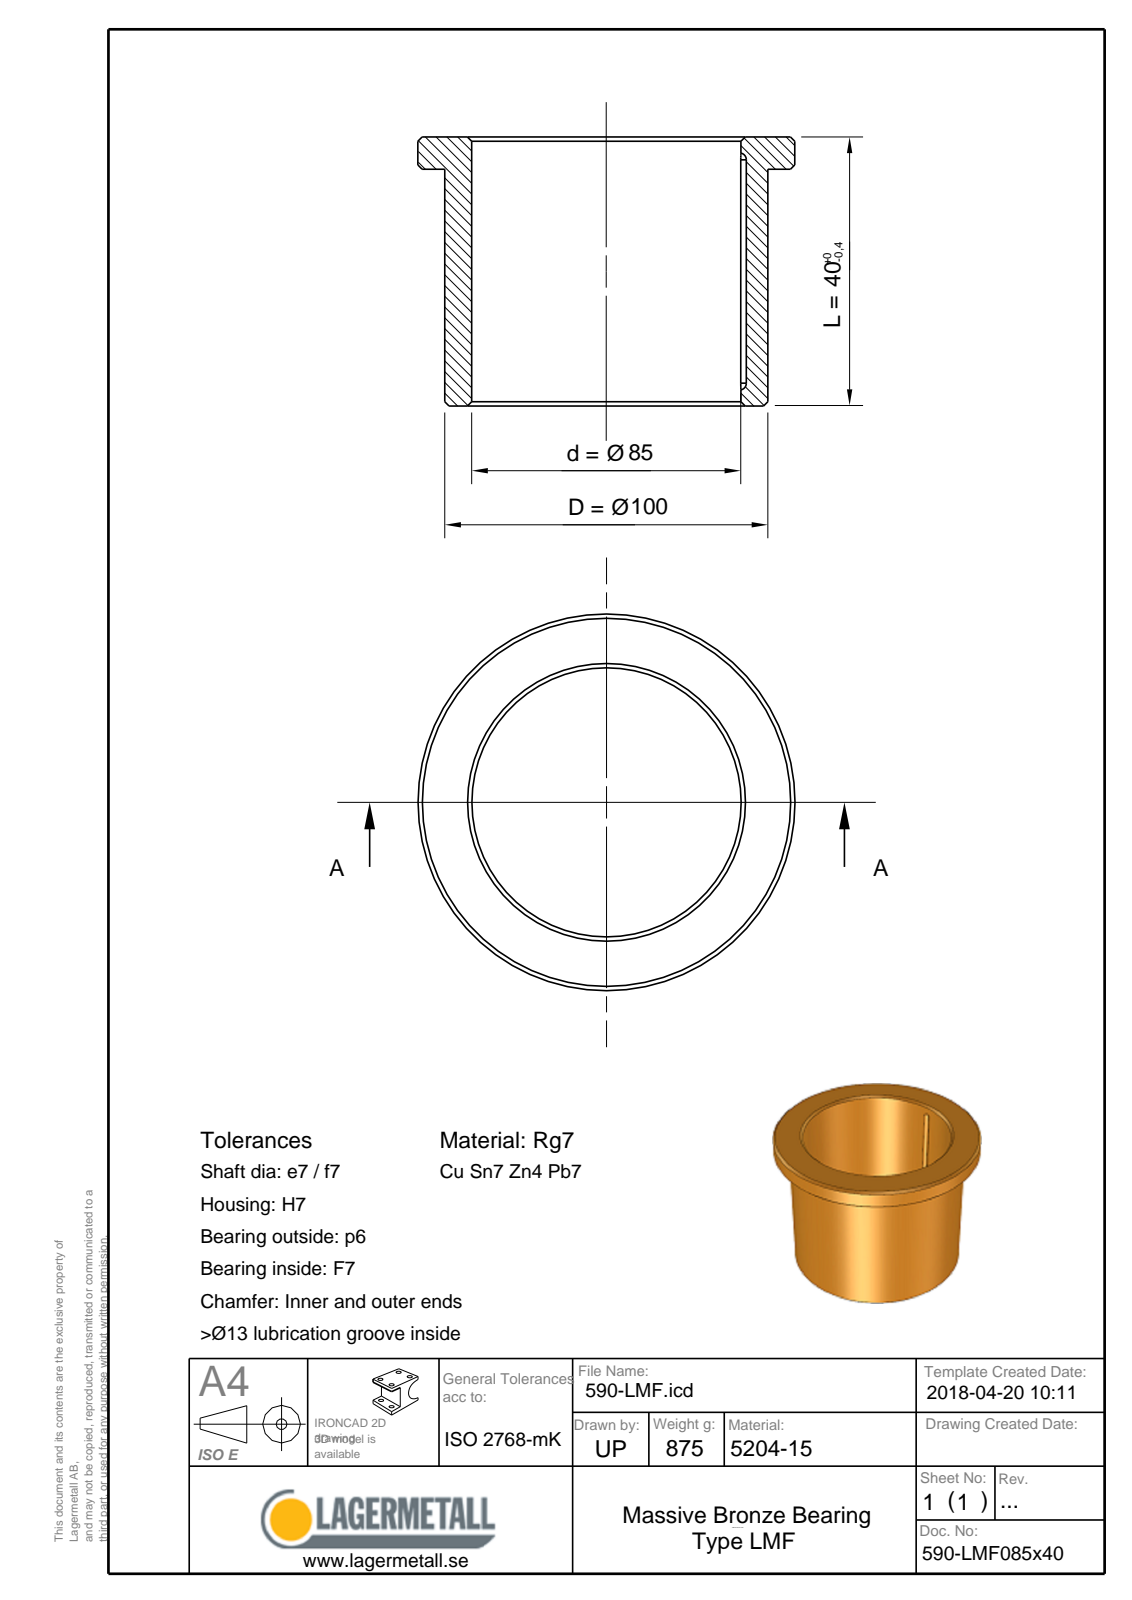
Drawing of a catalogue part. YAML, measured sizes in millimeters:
part_name: "590-LMF085x40"
step_written_by: "Spatial InterOp 3D (CONFIG_CONTROL_DESIGN)"
units: millimeters
bodies: {solids: 1, faces: 16, planar: 4, cylindrical: 5, other: 7}
overall_size: [110, 110, 40]
volume: 99483
surface_area: 30306
round_holes:
  - {diameter: 85, count: 1}
round_bosses_or_shafts:
  - {diameter: 110, count: 1}
  - {diameter: 100, count: 1}
partial_cylinders:
  - {radius: 1.75, count: 2}
face_to_face_distances: [40, 32, 8]
